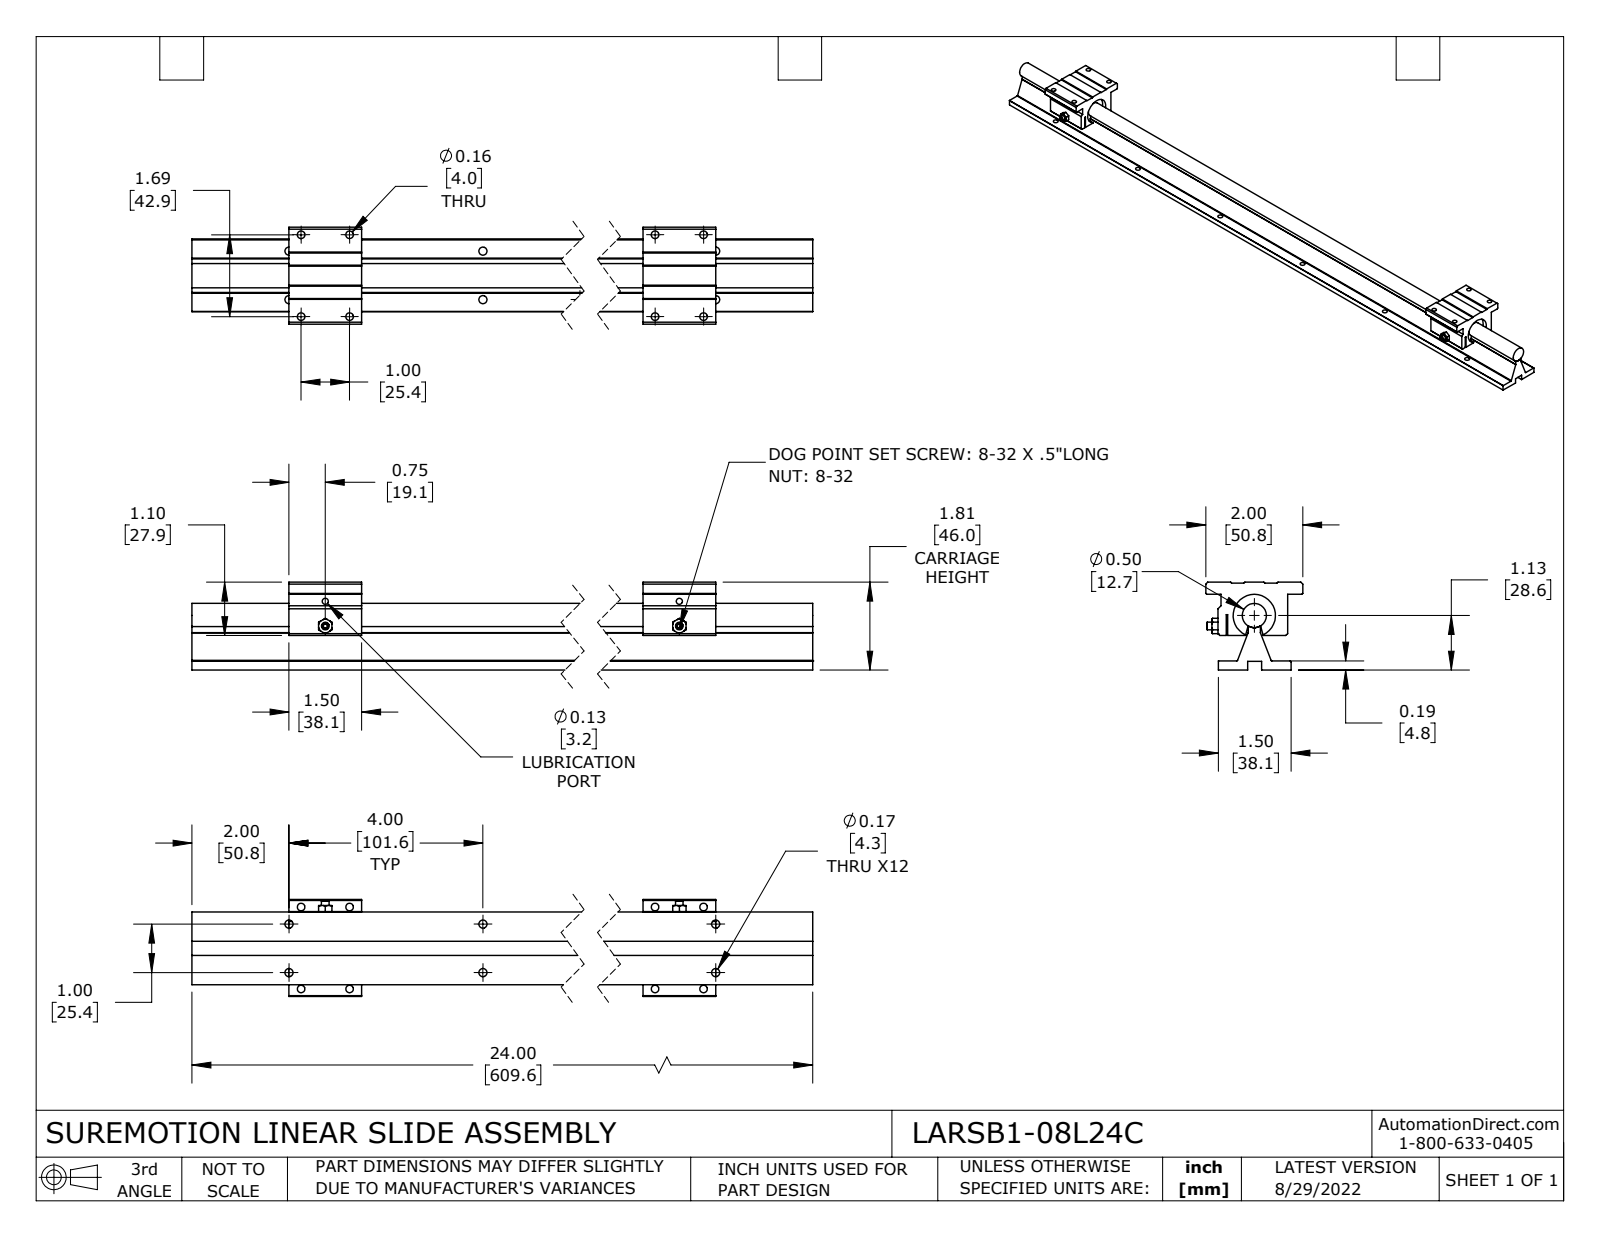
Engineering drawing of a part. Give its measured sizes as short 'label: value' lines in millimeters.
name: LARSACC-004; LARSB1-08L24C-RAIL; LARSB1-08L24C
written by: SolidWorks 2021 (CONFIG_CONTROL_DESIGN)
unit: mm
bodies: 4 solids, 216 faces (119 planar, 81 cylindrical, 16 other)
size: 609.6 × 50.8 × 46
volume: 353 000 mm³; area: 121 200 mm²
holes: 12× ⌀4.3, 8× ⌀4, 2× ⌀3.2, 2× ⌀12.7, 2× ⌀22.2
bosses: 2× ⌀4
rounds: 8× R0.5, 1× R1, 1× R6.3
face distances: 4.7, 15.4, 22.7, 4.6, 38.1, 6.4, 7.4, 16.1, 22.4, 0.7
hole spacings: 25.4, 101.6, 104.7, 203.2, 204.8, 304.8, 305.9, 469.9
